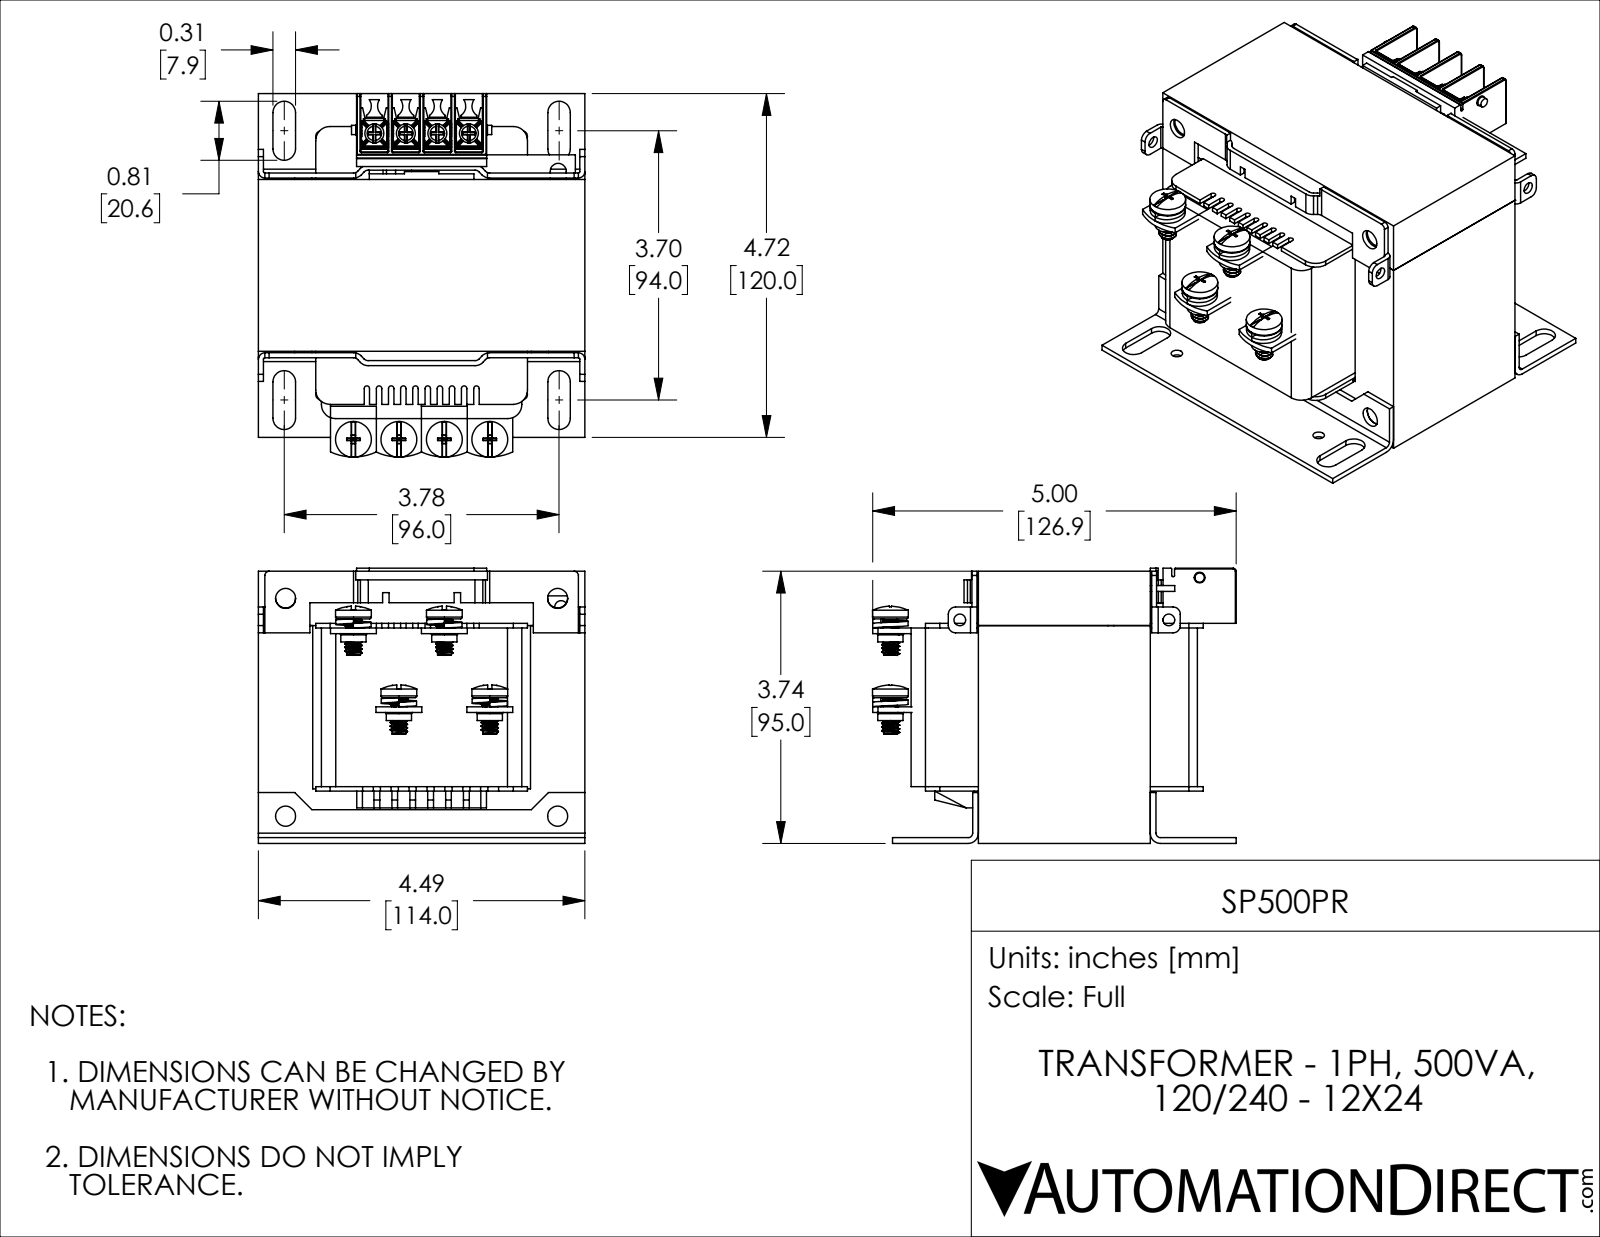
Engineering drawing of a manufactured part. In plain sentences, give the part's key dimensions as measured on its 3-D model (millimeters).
The part is named "SP500PR". Its 3-D file was written by "SolidWorks 2018 (AUTOMOTIVE_DESIGN)". It is 37 solids with 2386 faces: 1356 planar, 796 cylindrical and 234 other. Overall it measures 127 by 114 by 96 millimeters. Its volume is 826 700 cubic millimeters and its surface area 174 600 square millimeters. Round holes: 9 of diameter 4, 6 of diameter 7, 4 of diameter 2.7, 4 of diameter 3.5, 4 of diameter 6.4, 4 of diameter 6.8, 2 of diameter 4.1, 2 of diameter 4.5. Round bosses or shafts: 4 of diameter 12.5, 4 of diameter 12.3, 4 of diameter 8.8, 4 of diameter 6.7, 4 of diameter 6.1, 4 of diameter 4.8, 4 of diameter 4.3, 4 of diameter 2.8. Partial cylindrical surfaces (rounded edges, fillets, slot ends): 34 of radius 0.1, 31 of radius 0.3, 21 of radius 0.3, 20 of radius 0.9, 16 of radius 0.7, 10 of radius 0.9, 9 of radius 2, 8 of radius 0.4. The main face-to-face distances are 76, 19, 95, 22, 60, 92, 76.5, 38, 2, 57. The hole center spacings are 11, 22, 95, 33, 40.5, 51.5, 15.9, 18.5.
